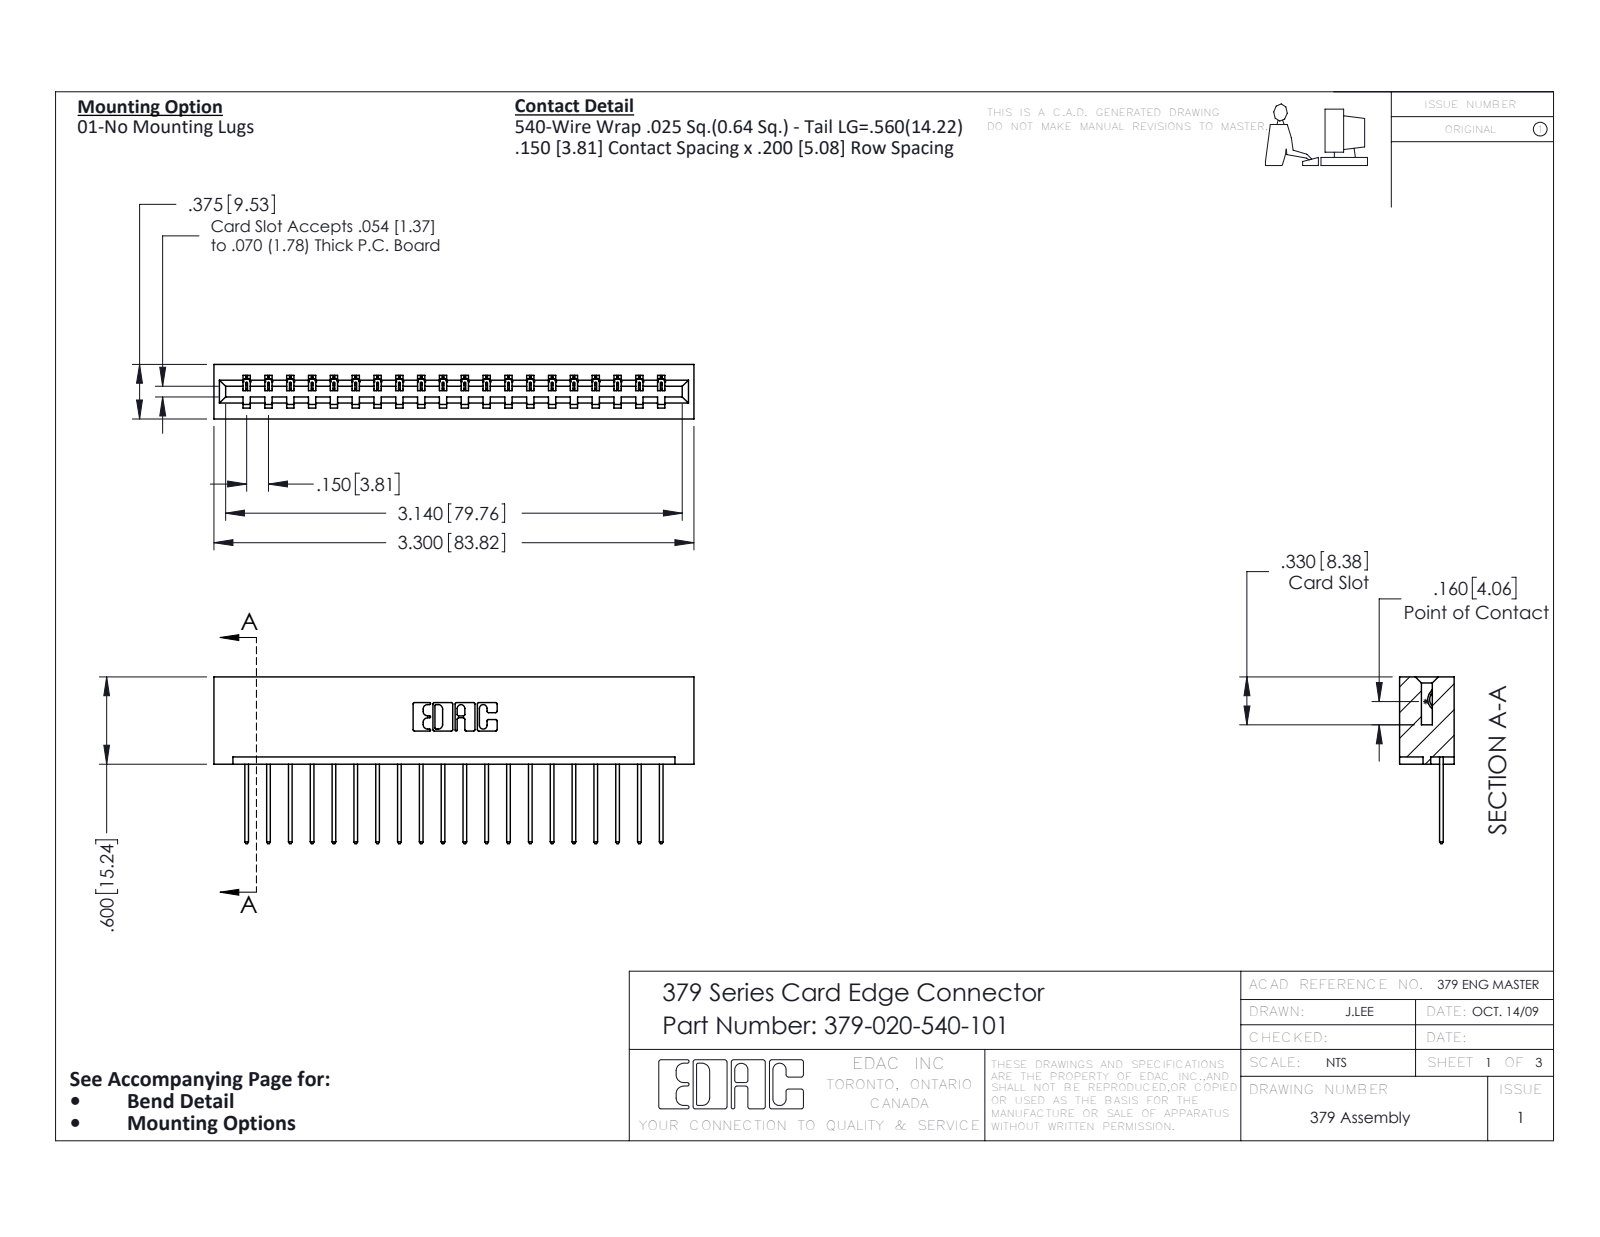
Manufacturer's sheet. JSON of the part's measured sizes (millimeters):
{"part_name": "379-020-540-101; 345-292-001_345-293-140; 379 Part_Lugless", "step_written_by": "SolidWorks 2016 (CONFIG_CONTROL_DESIGN)", "units": "millimeters", "bodies": {"solids": 21, "faces": 1266, "planar": 906, "cylindrical": 360, "other": 0}, "overall_size": [83.8, 29.1, 9.5], "volume_mm3": 9290, "surface_area_mm2": 9561, "partial_cylinders_radius": [[0.2, 40], [0.3, 40], [0.3, 22], [0.2, 6], [0.8, 6], [0.7, 3], [0.4, 1], [0.6, 1]], "face_to_face_distances": [7.6, 1.9, 9.5, 15.2, 5.7, 3.8, 11.4, 2.5, 7, 0.6]}
